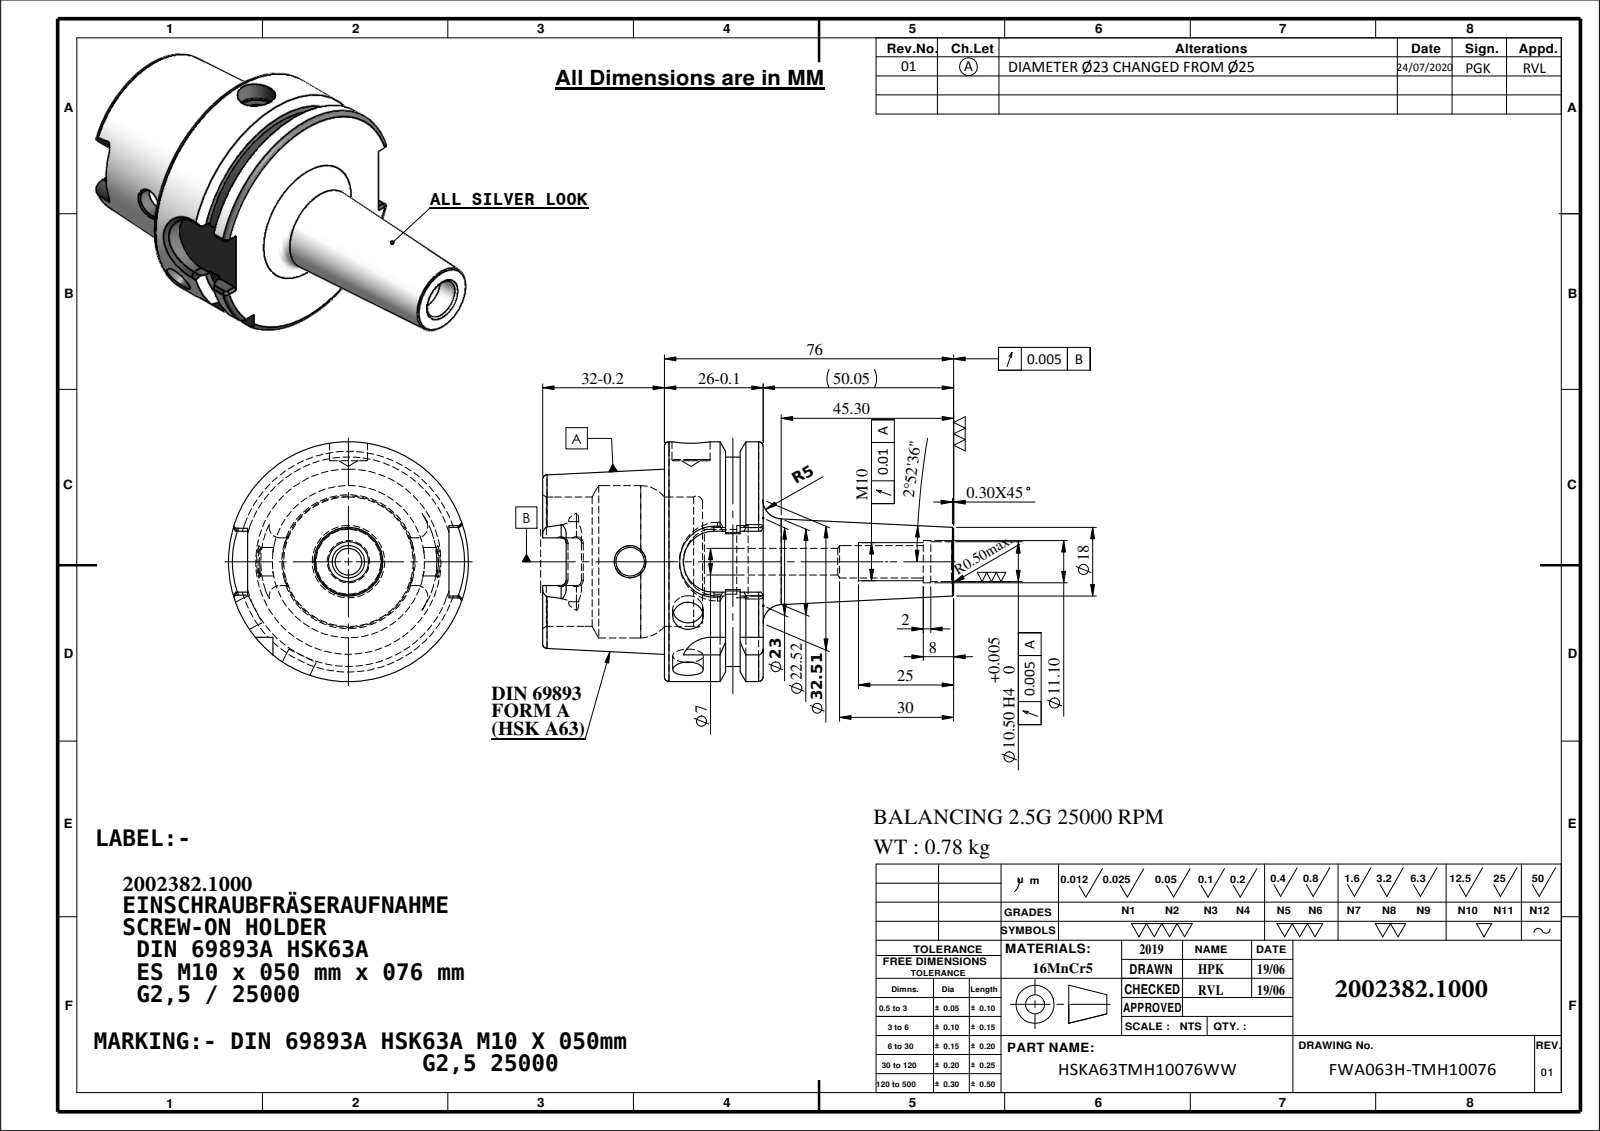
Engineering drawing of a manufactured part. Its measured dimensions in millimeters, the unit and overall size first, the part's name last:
Units: millimetres
Overall size (bounding box): 108 × 63 × 63
Round holes (diameter × count): ⌀8 ×2, ⌀7 ×1, ⌀7.5 ×1, ⌀8.5 ×1, ⌀10 ×1, ⌀10.5 ×1, ⌀11.1 ×1, ⌀17 ×1, ⌀19 ×1, ⌀34 ×1, ⌀40 ×1
Round bosses / shafts (diameter × count): ⌀63 ×1, ⌀55 ×1
Partial cylindrical surfaces — rounded edges, fillets, slot ends (radius × count): R1.3 ×6, R2.88 ×4, R8 ×2, R9 ×1
Main face-to-face distances: 25.95, 10, 15.95, 32, 42, 57.95, 54, 52.9, 22, 12
Volume: 95 089 mm³ · Surface area: 26 584 mm²
Bodies: 1 solid, 168 faces (51 planar, 51 cylindrical, 66 other)
Part name (STEP PRODUCT): 9163A-ES8M10050
STEP written by: SolidWorks 2018 (AUTOMOTIVE_DESIGN)
